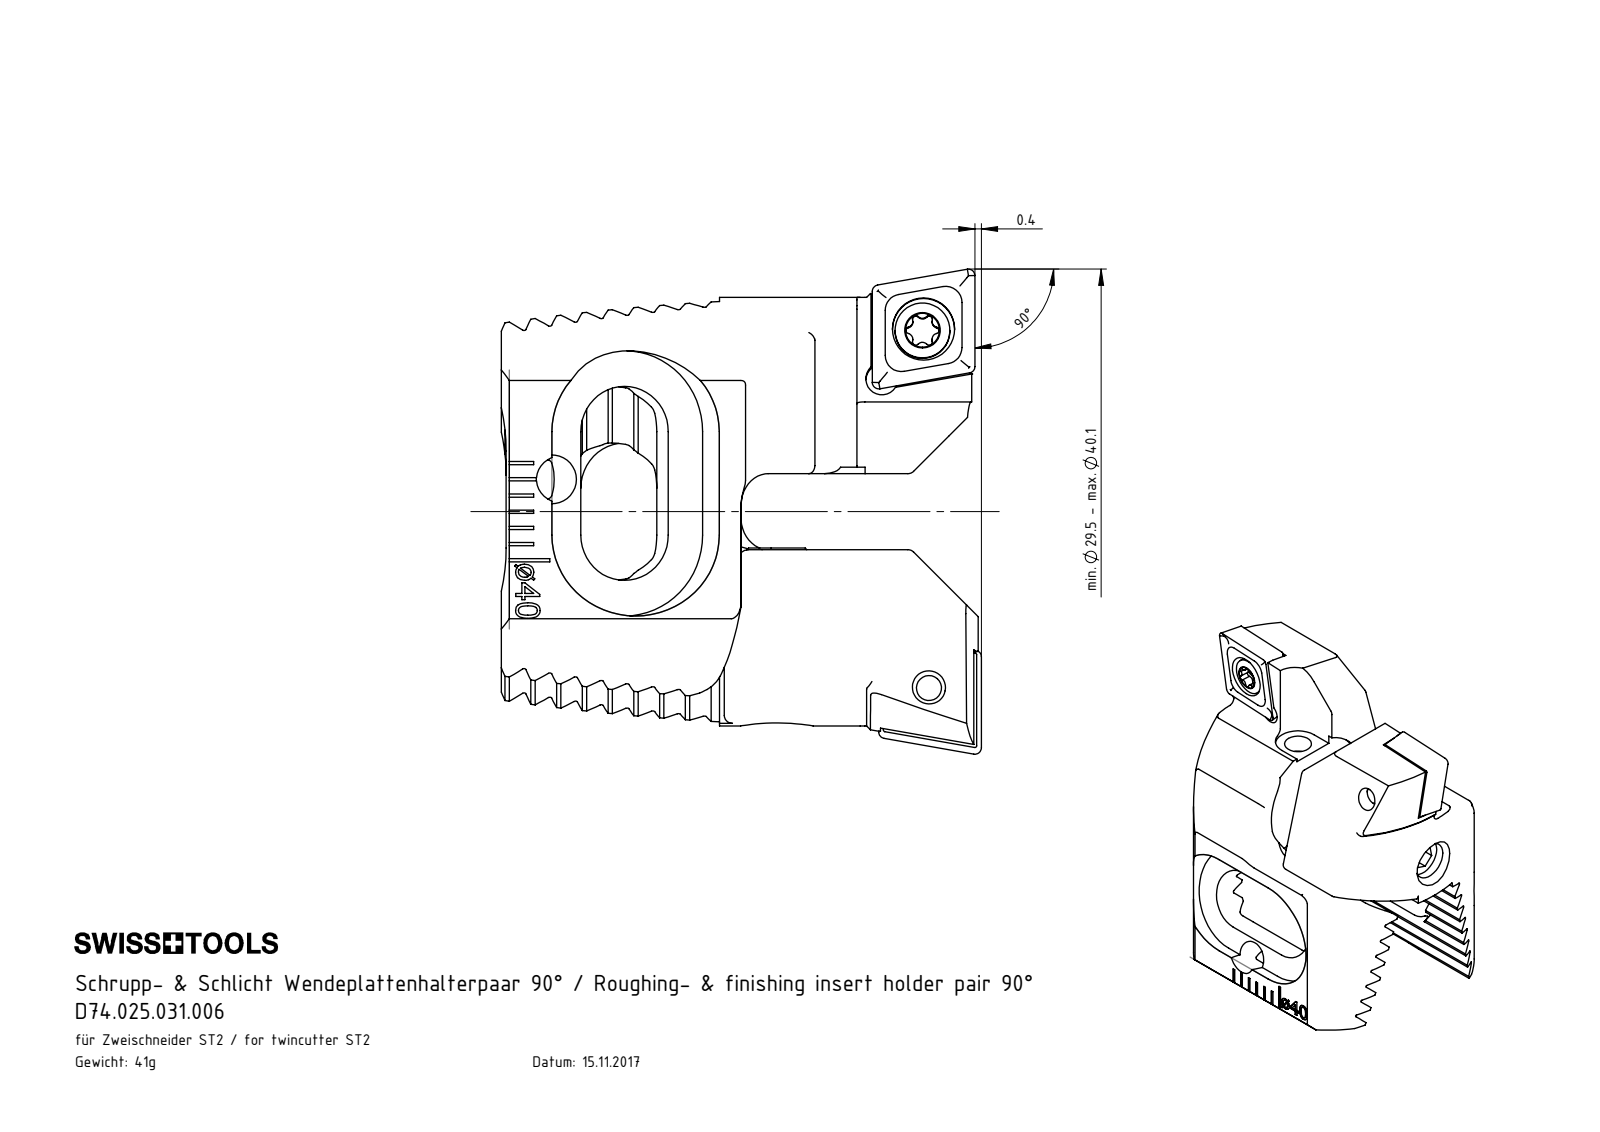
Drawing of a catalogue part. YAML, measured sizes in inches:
part_name: "ZC2-xxx.001.016_A_versetzt Combi; WCA-ER2.001.006_A; CCMT060204; ISO 4028 - M3 x 5_M3x6 (+3 more)"
step_written_by: "SolidWorks 2017 (CONFIG_CONTROL_DESIGN)"
units: inches
bodies: {solids: 8, faces: 653, planar: 328, cylindrical: 143, other: 182}
overall_size: [1.181, 1.169, 0.799]
volume: 0.314
surface_area: 7.266
round_holes:
  - {diameter: 0.079, count: 2}
  - {diameter: 0.081, count: 2}
  - {diameter: 0.11, count: 2}
  - {diameter: 0.152, count: 2}
  - {diameter: 0.063, count: 1}
  - {diameter: 0.098, count: 1}
  - {diameter: 0.118, count: 1}
  - {diameter: 0.138, count: 1}
round_bosses_or_shafts:
  - {diameter: 0.134, count: 2}
  - {diameter: 0.098, count: 2}
  - {diameter: 0.157, count: 1}
  - {diameter: 0.118, count: 1}
  - {diameter: 0.079, count: 1}
partial_cylinders:
  - {radius: 0.02, count: 18}
  - {radius: 0.005, count: 16}
  - {radius: 0.008, count: 12}
  - {radius: 0.014, count: 10}
  - {radius: 0.079, count: 4}
  - {radius: 0.11, count: 4}
  - {radius: 0.197, count: 4}
  - {radius: 0.472, count: 4}
face_to_face_distances: [0.056, 0.113, 0.169, 0.225, 0.281, 0.154, 0.338, 0.04, 0.016, 0.201]
hole_center_spacings: [0.154, 0.157, 0.276, 0.646, 0.768, 0.772, 0.772, 0.776]
